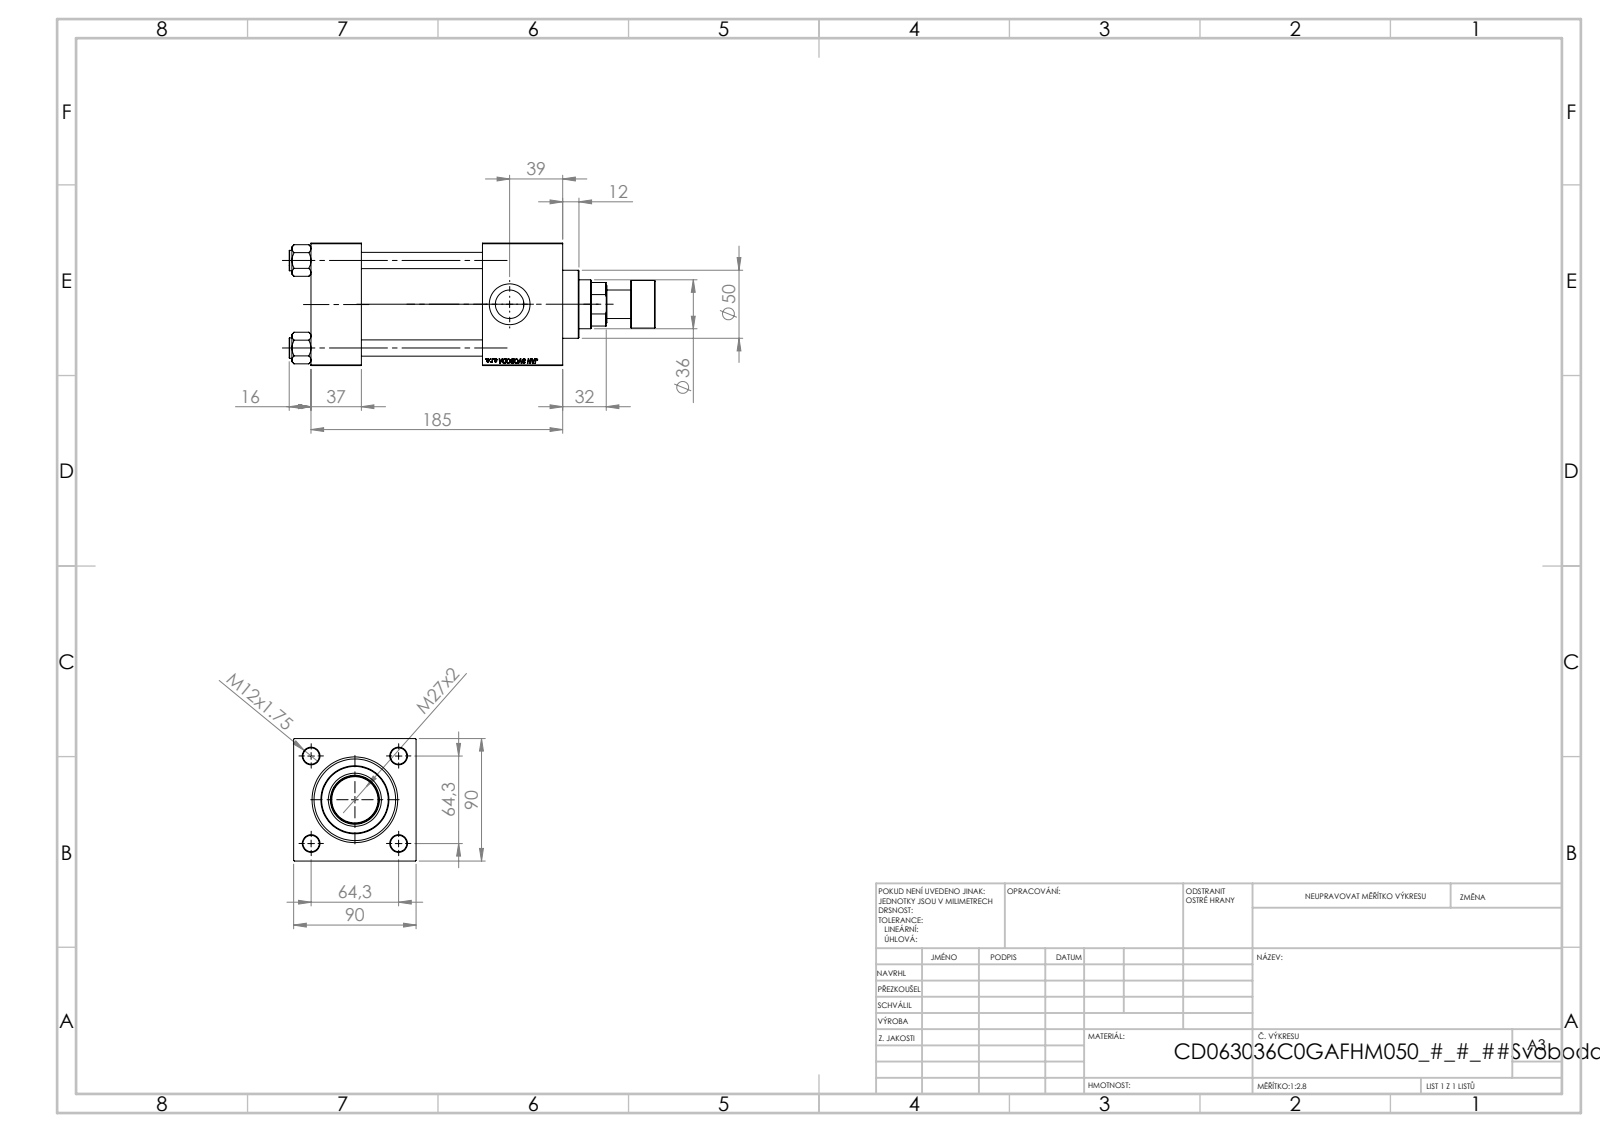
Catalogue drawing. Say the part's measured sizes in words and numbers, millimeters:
The part is named "V215CD_C_TYCINKA; NUT_M5_V215CD_C; V215CD_VC_C; V215CD_Body_C (+2 more)". Its 3-D file was written by "SolidWorks 2019 (CONFIG_CONTROL_DESIGN)". It is 12 solids with 1163 faces: 530 planar, 91 cylindrical and 542 other. Overall it measures 269 by 90 by 90 millimeters. Its volume is 1 054 000 cubic millimeters and its surface area 210 163 square millimeters. Round holes: 4 of diameter 12, 2 of diameter 7, 2 of diameter 20.96, 2 of diameter 30, 1 of diameter 25.5, 1 of diameter 36, 1 of diameter 39, 1 of diameter 50, 1 of diameter 60, 1 of diameter 63. Round bosses or shafts: 4 of diameter 15, 1 of diameter 69, 1 of diameter 35, 1 of diameter 21. The main face-to-face distances are 90, 37, 185, 148, 59, 126, 89, 50, 109, 156.3. The hole center spacings are 45.47, 64.3, 90.93.
